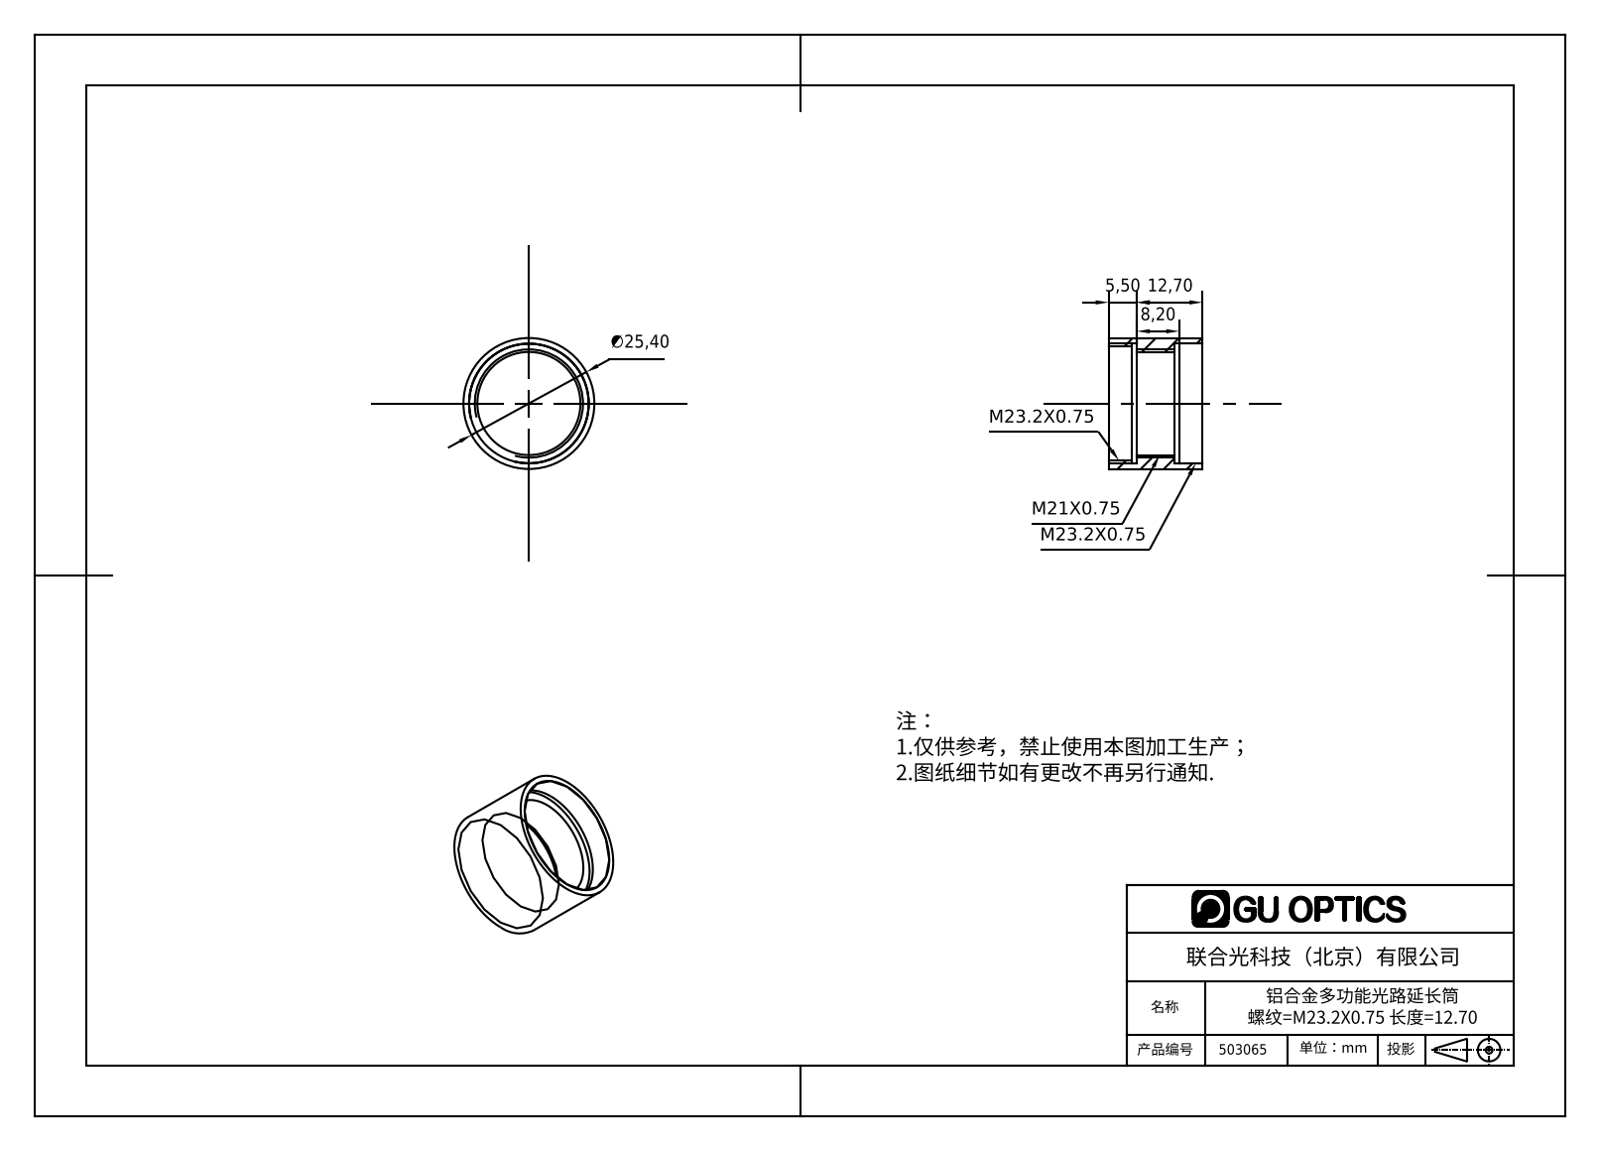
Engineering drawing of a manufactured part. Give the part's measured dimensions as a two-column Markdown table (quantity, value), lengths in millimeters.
| quantity | value |
| --- | --- |
| part name | 503065 |
| STEP written by | SolidWorks 2016 (AUTOMOTIVE_DESIGN) |
| units | millimeters |
| bodies | 1 solid, 18 faces (6 planar, 12 cylindrical, 0 other) |
| overall size | 25.4 × 25.4 × 18.2 |
| volume | 2 456 mm³ |
| surface area | 3 179 mm² |
| round holes (diameter × count) | 20 × 1, 22.2 × 1, 23.2 × 1, 23.4 × 1 |
| round bosses / shafts (diameter × count) | 25.4 × 1 |
| main face-to-face distances | 5.5, 12.7, 7.2, 18.2, 4.5, 13.7, 1, 8.2, 9.2 |
